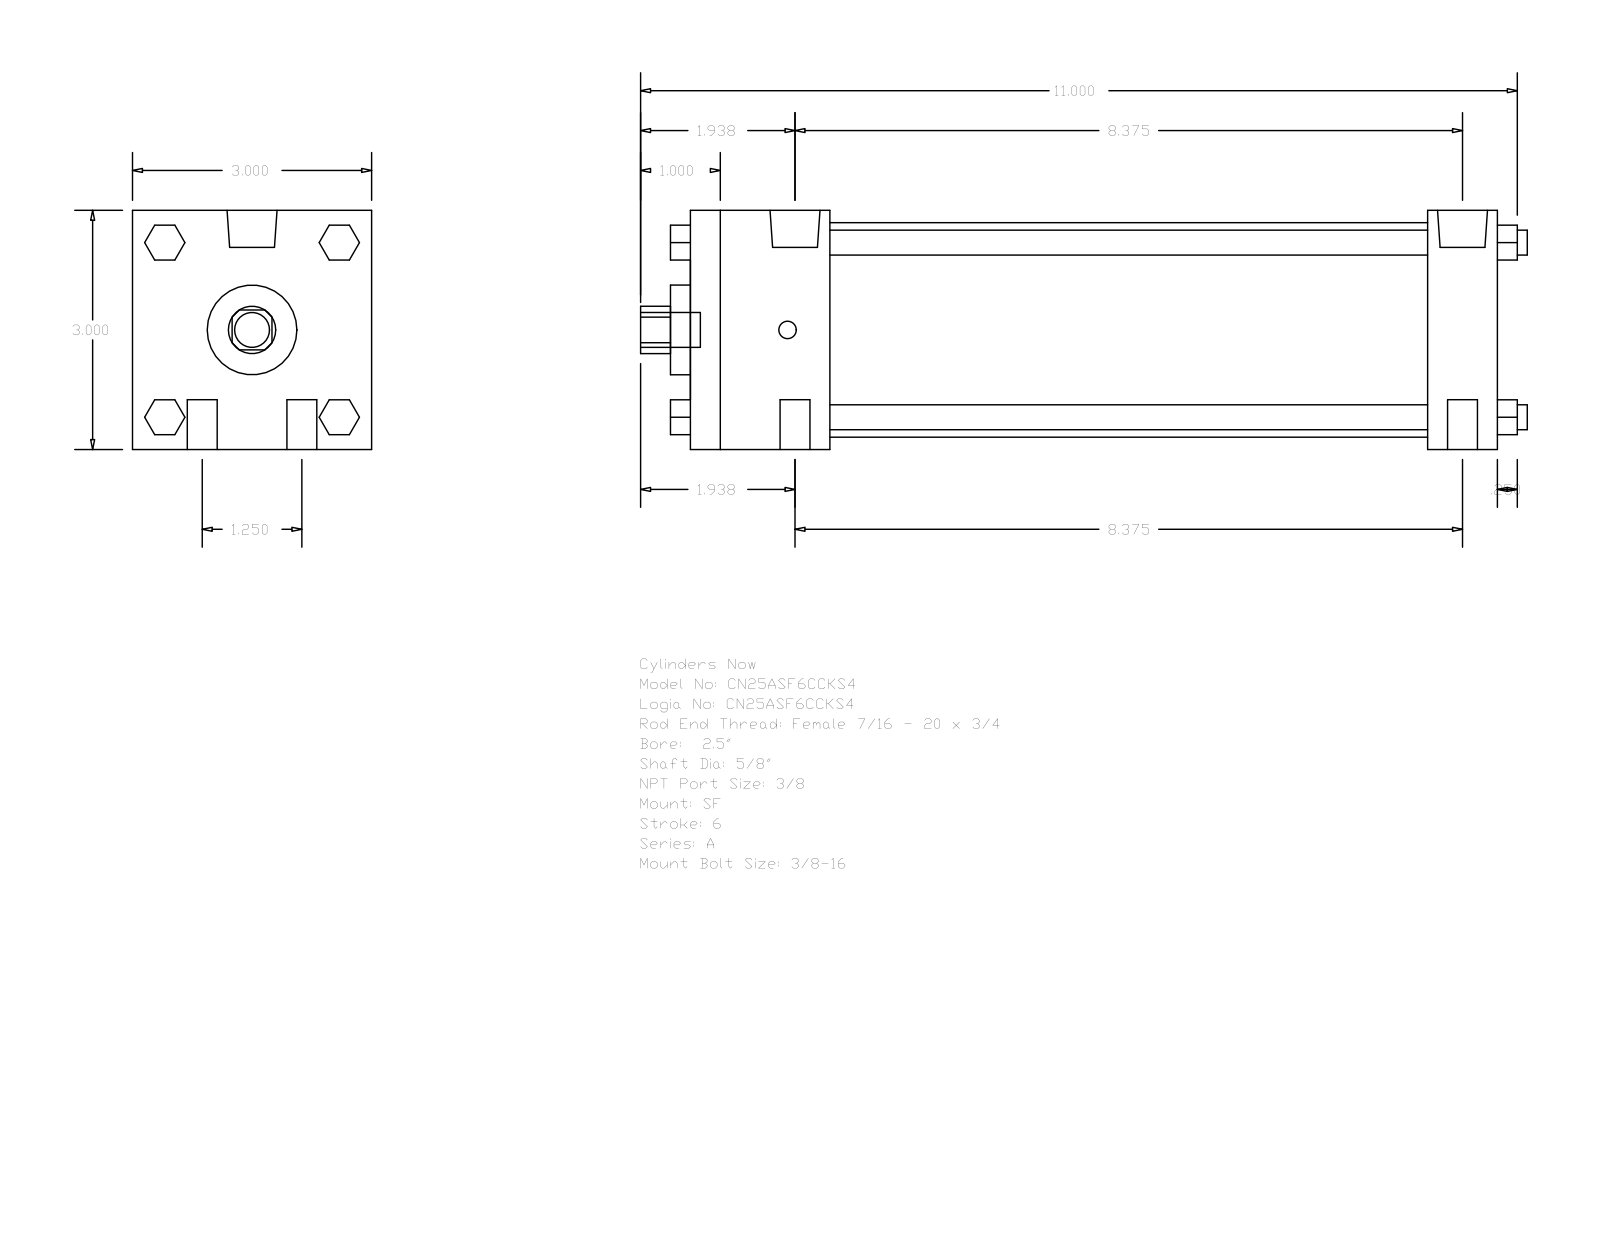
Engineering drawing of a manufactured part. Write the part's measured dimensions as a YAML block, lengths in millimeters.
part_name: "A_SF__0250_0.625"
step_written_by: "GSSL Pune (CONFIG_CONTROL_DESIGN)"
units: millimeters
bodies: {solids: 0, faces: 124, planar: 94, cylindrical: 30, other: 0}
overall_size: [282.57, 76.2, 76.2]
round_holes:
  - {diameter: 15.88, count: 1}
  - {diameter: 28.57, count: 1}
  - {diameter: 68.33, count: 1}
round_bosses_or_shafts:
  - {diameter: 9.53, count: 4}
  - {diameter: 7.94, count: 4}
  - {diameter: 15.93, count: 2}
  - {diameter: 5.56, count: 2}
  - {diameter: 11.11, count: 1}
partial_cylinders:
  - {radius: 7.54, count: 1}
face_to_face_distances: [76.2, 257.17, 44.45, 234.94, 22.23, 190.49, 212.72, 263.52, 6.35, 50.8]
